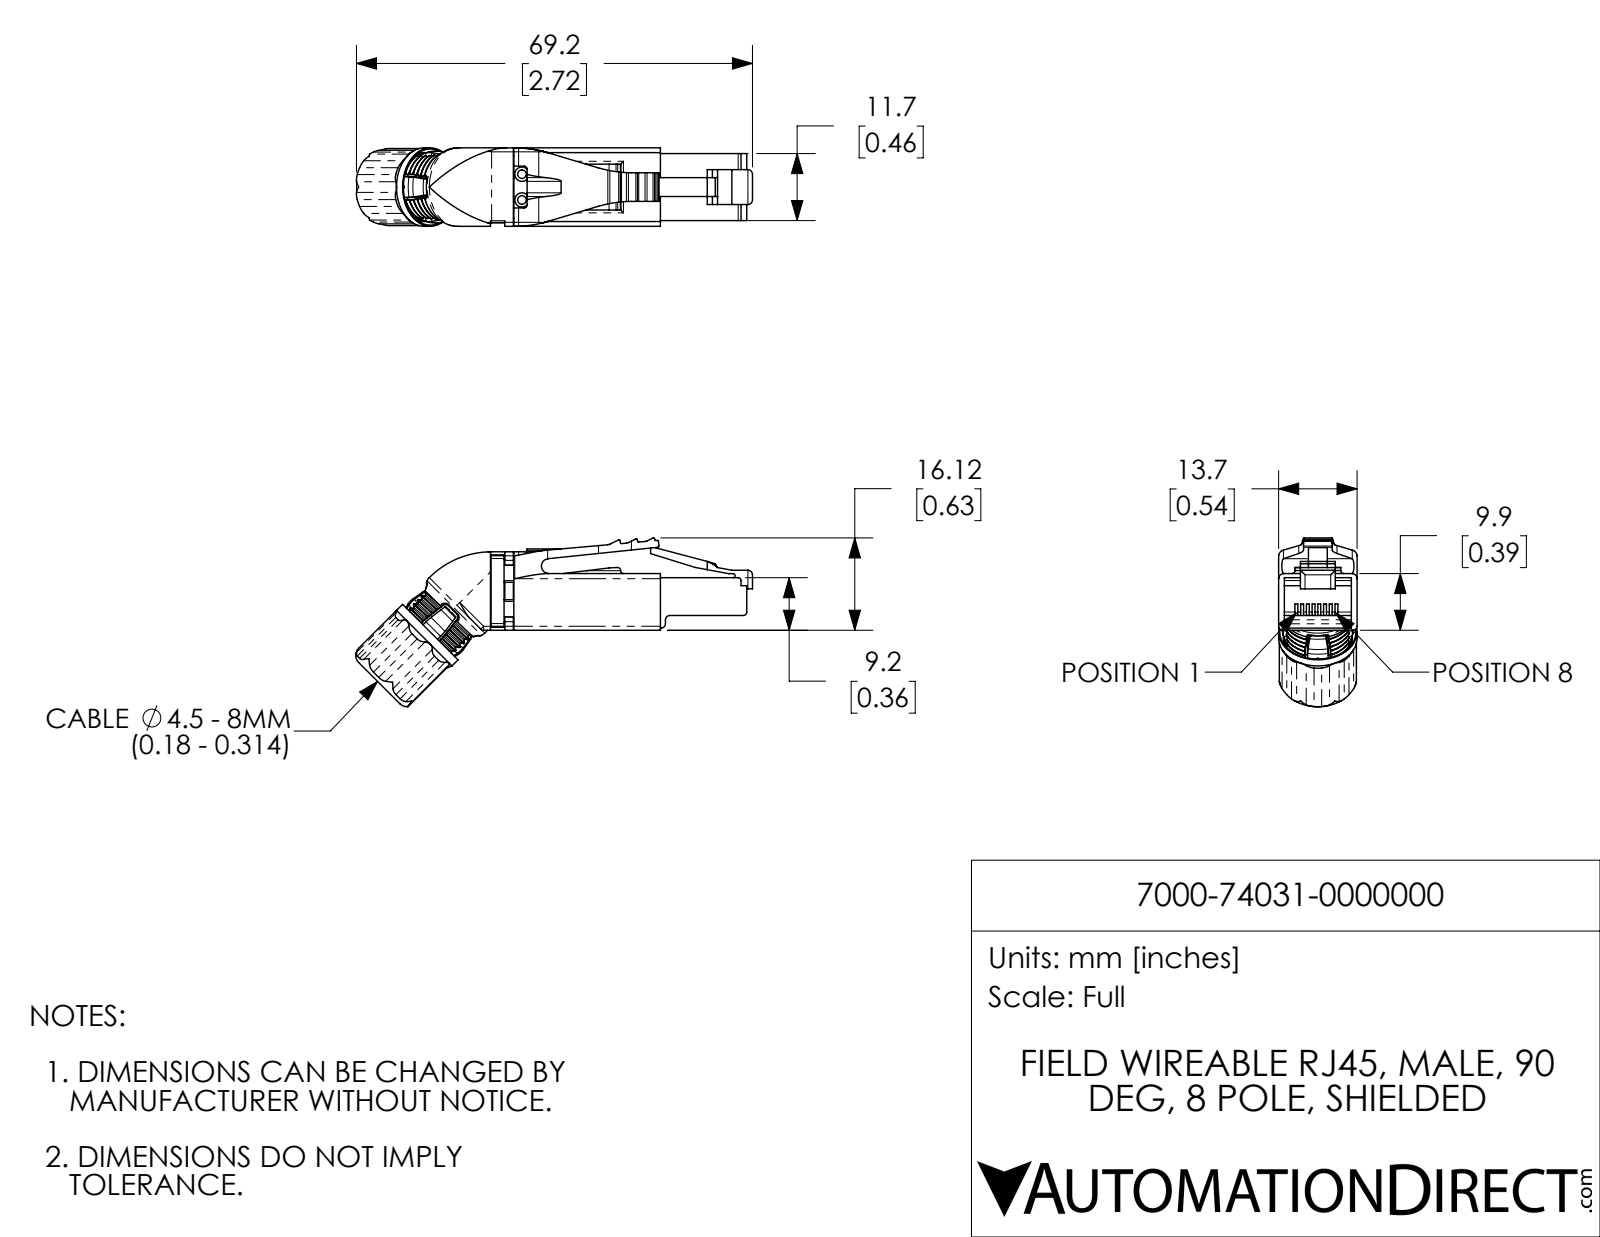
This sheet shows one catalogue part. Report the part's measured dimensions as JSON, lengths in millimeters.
{"part_name": "7000-74031-0000000", "step_written_by": "SolidWorks 2017 (AUTOMOTIVE_DESIGN)", "units": "millimeters", "bodies": {"solids": 1, "faces": 636, "planar": 197, "cylindrical": 249, "other": 190}, "overall_size": [69.3, 29.5, 13.7], "volume_mm3": 9230, "surface_area_mm2": 5025, "round_holes": [[1.5, 2], [9.6, 1]], "round_bosses_or_shafts": [[13.7, 1]], "partial_cylinders_radius": [[10, 21], [0.7, 17], [1, 11], [0.3, 10], [0.5, 9], [0.2, 8], [0.3, 8], [3, 8]], "face_to_face_distances": [13.7, 1, 12.7, 6.6, 9.2, 2.6, 9.9, 7.3, 0.7, 2], "hole_center_spacings": [4.5]}
